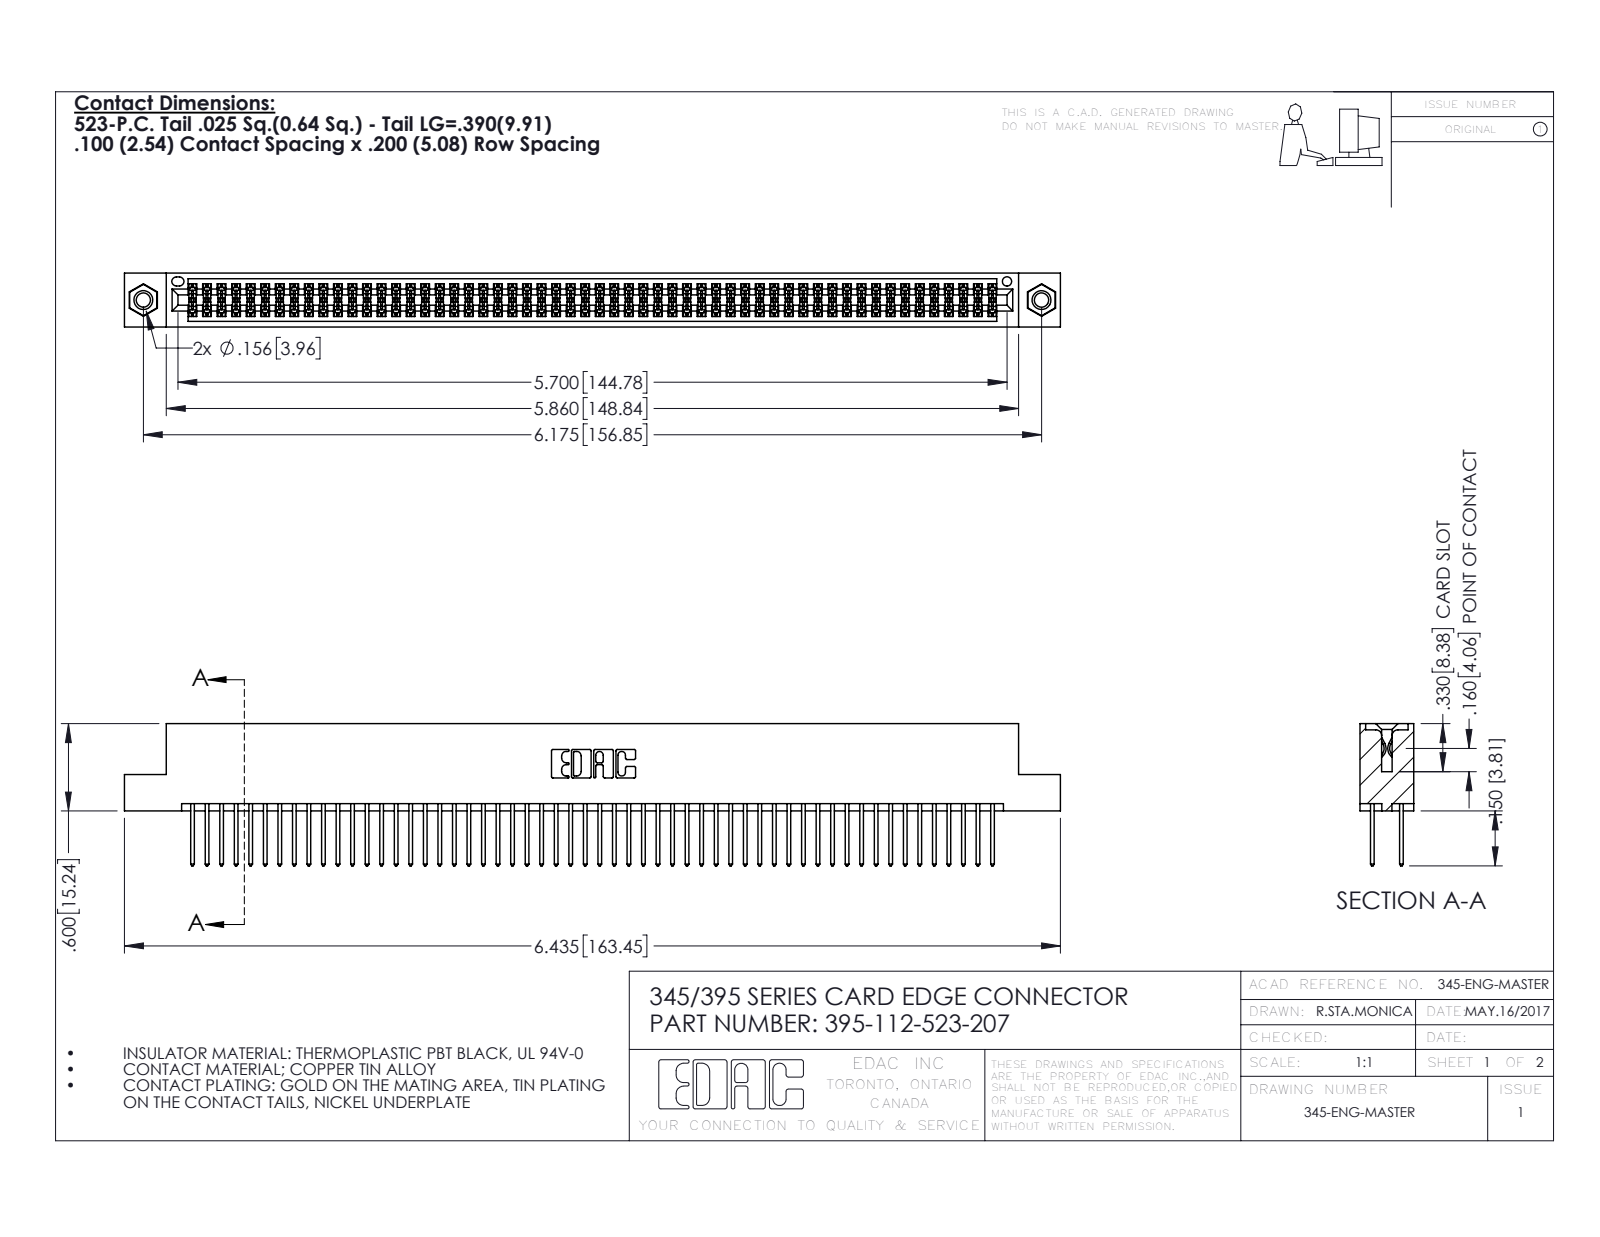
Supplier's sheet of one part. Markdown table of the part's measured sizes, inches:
| quantity | value |
| --- | --- |
| part name | 395-112-523-207; 345-250-001_345-250-005-103; 345-292-001_345-293-123; 345 Part_Flush Mounting Lugs - 0.156 Dia-TI |
| STEP written by | SolidWorks 2016 (CONFIG_CONTROL_DESIGN) |
| units | inches |
| bodies | 115 solids, 5786 faces (3808 planar, 1962 cylindrical, 16 other) |
| overall size | 6.435 × 0.977 × 0.37 |
| volume | 0.99 in³ |
| surface area | 39.23 in² |
| round holes (diameter × count) | 0.098 × 2, 0.125 × 2, 0.156 × 2, 0.064 × 1 |
| round bosses / shafts (diameter × count) | 0.155 × 2 |
| partial cylindrical surfaces (radius × count) | 0.006 × 168, 0.01 × 112, 0.01 × 22, 0.007 × 6, 0.031 × 6, 0.026 × 3, 0.014 × 2, 0.019 × 2 |
| main face-to-face distances | 0.072, 0.298, 0.2, 0.098, 0.272, 0.025, 0.37, 0.225, 0.175, 0.149 |
| hole center spacings | 0.27, 5.939, 6.175 |
